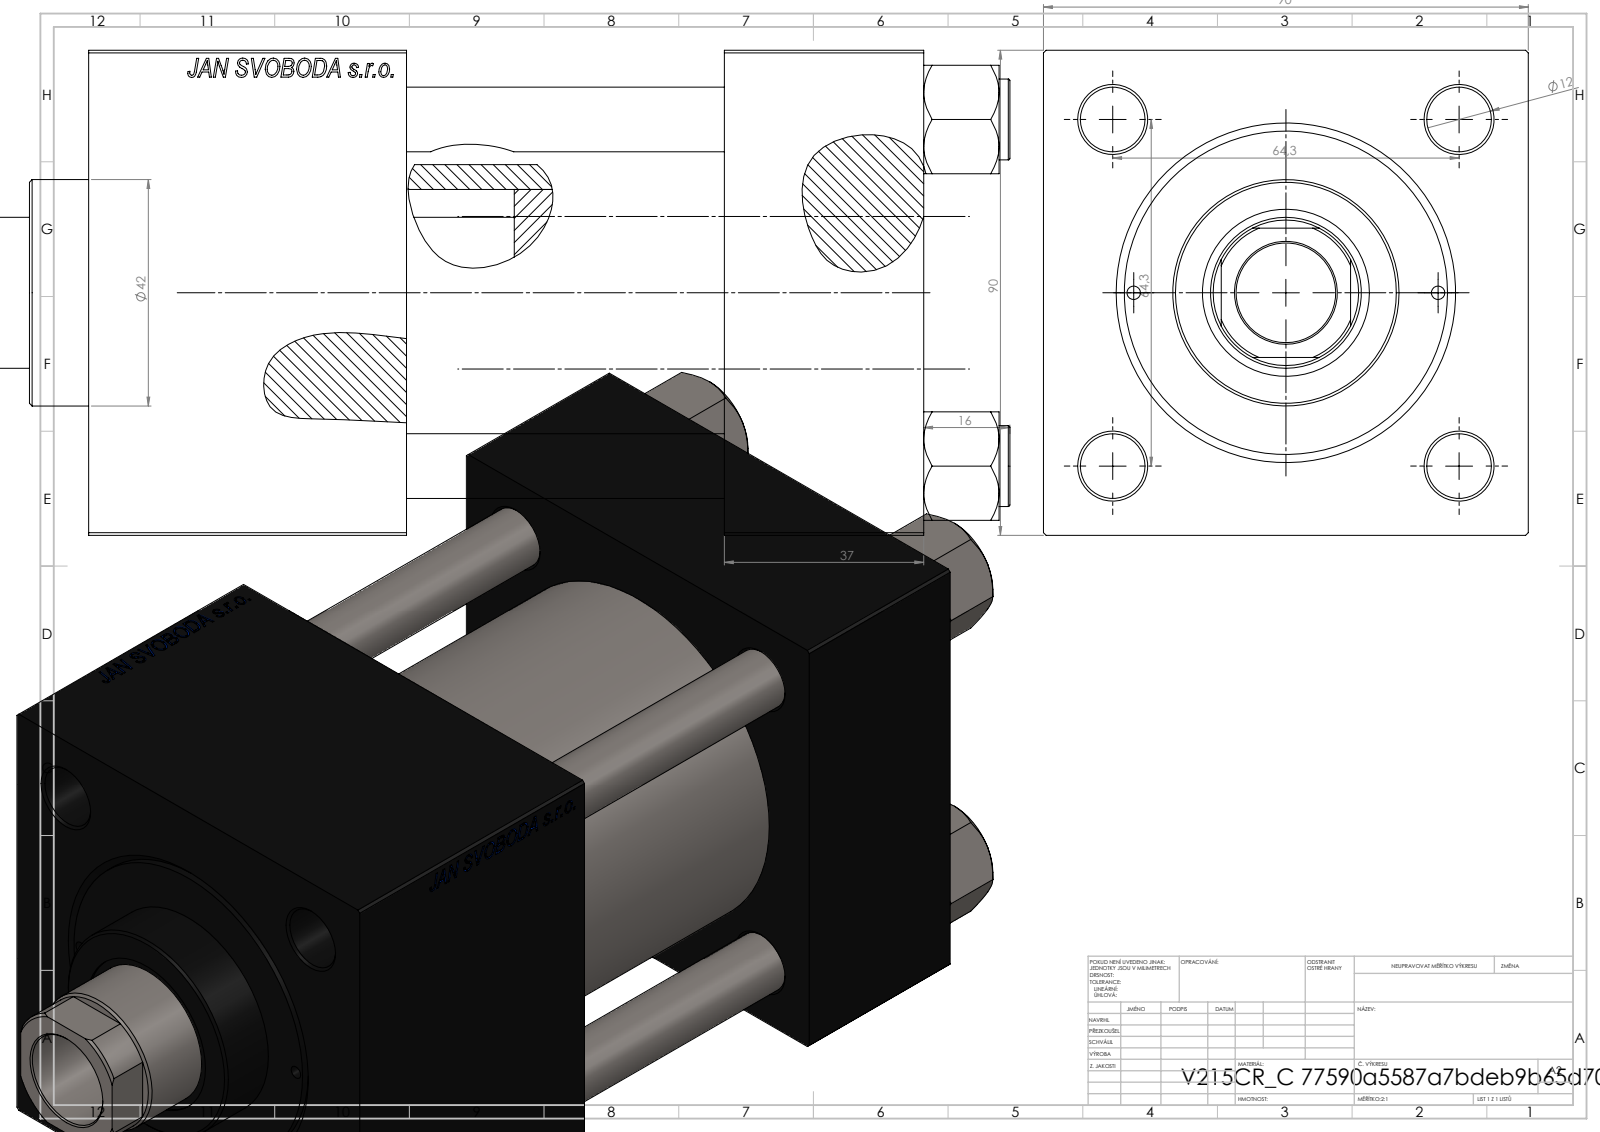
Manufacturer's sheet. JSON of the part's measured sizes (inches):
{"part_name": "V215CR_C_TYCINKA; NUT_M5_C; V215CR_C_Body; V215CR_VCP_C (+1 more)", "step_written_by": "SolidWorks 2019 (CONFIG_CONTROL_DESIGN)", "units": "inches", "bodies": {"solids": 11, "faces": 1154, "planar": 528, "cylindrical": 90, "other": 536}, "overall_size": [7.992, 3.543, 3.543], "volume_in3": 57.78, "surface_area_in2": 277.8, "round_holes": [[0.472, 4], [0.098, 2], [0.276, 2], [0.825, 2], [1.181, 2], [0.728, 1], [1.102, 1], [1.22, 1], [1.969, 1], [2.362, 1], [2.48, 1]], "round_bosses_or_shafts": [[0.591, 4], [2.717, 1], [1.654, 1]], "partial_cylinders_radius": [[0.531, 1]], "face_to_face_distances": [3.543, 2.323, 1.457, 6.102, 4.646, 3.78, 4.972, 3.516, 1.193, 1.13], "hole_center_spacings": [1.275, 1.79, 2.531, 2.694, 1.112, 3.58, 2.224, 3.839]}
